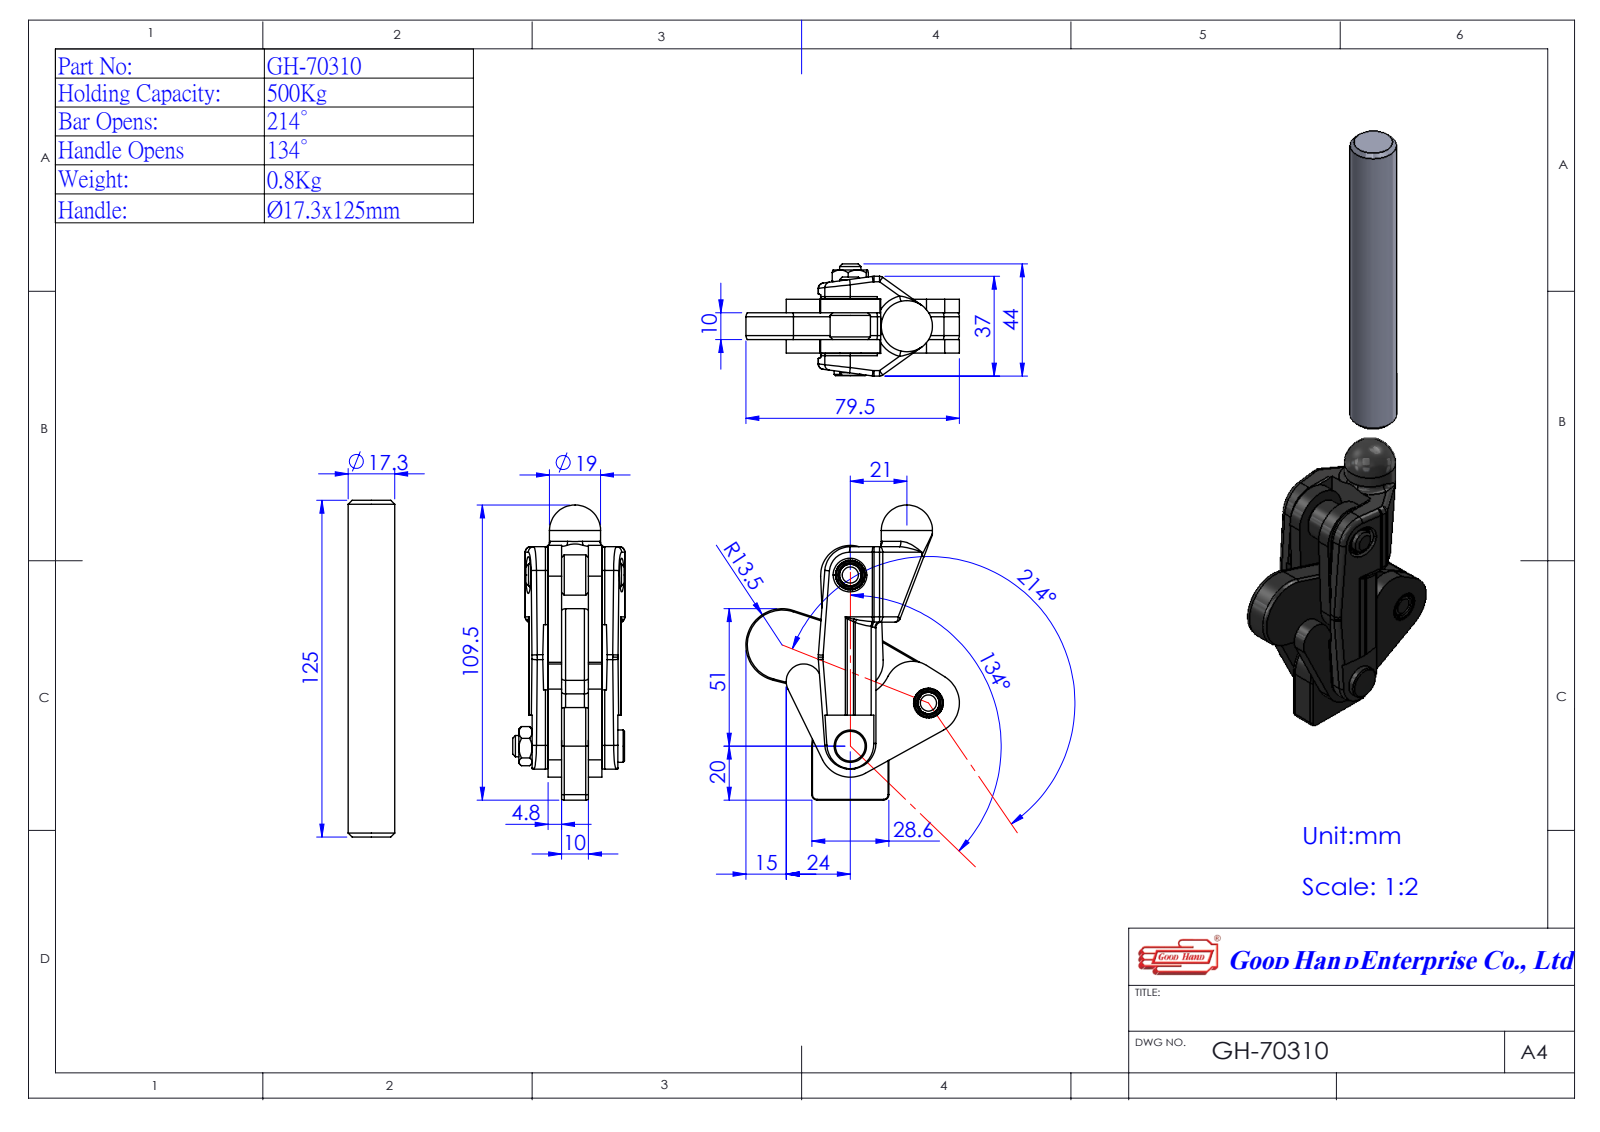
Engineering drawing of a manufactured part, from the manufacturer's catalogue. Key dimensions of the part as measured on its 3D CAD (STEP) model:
Part name (STEP PRODUCT): Group2^GH-70310(簡化); 17031001-1^GH-70310(簡化); Group1^GH-70310(簡化); 37031013-1^GH-70310(簡化) (+3 more)
STEP written by: SolidWorks 2016 (AUTOMOTIVE_DESIGN)
Units: millimetres
Bodies: 6 solids, 214 faces (71 planar, 94 cylindrical, 49 other)
Overall size (bounding box): 233.72 × 79.27 × 41.6
Volume: 106 958 mm³ · Surface area: 48 526 mm²
Round holes (diameter × count): ⌀8 ×4, ⌀12.5 ×1
Round bosses / shafts (diameter × count): ⌀8.18 ×2, ⌀19 ×1, ⌀17.3 ×1, ⌀15 ×1, ⌀12 ×1, ⌀7.94 ×1
Partial cylindrical surfaces — rounded edges, fillets, slot ends (radius × count): R2 ×22, R5 ×6, R9.5 ×2, R11 ×2, R11.5 ×2, R6.5 ×1, R10 ×1, R12 ×1
Main face-to-face distances: 5, 15, 10, 5.1, 15.1, 4.98, 14.98, 5.02, 15.02, 20
Hole centre spacings: 31.54, 31.81, 32, 33.12, 55.65, 63.5
